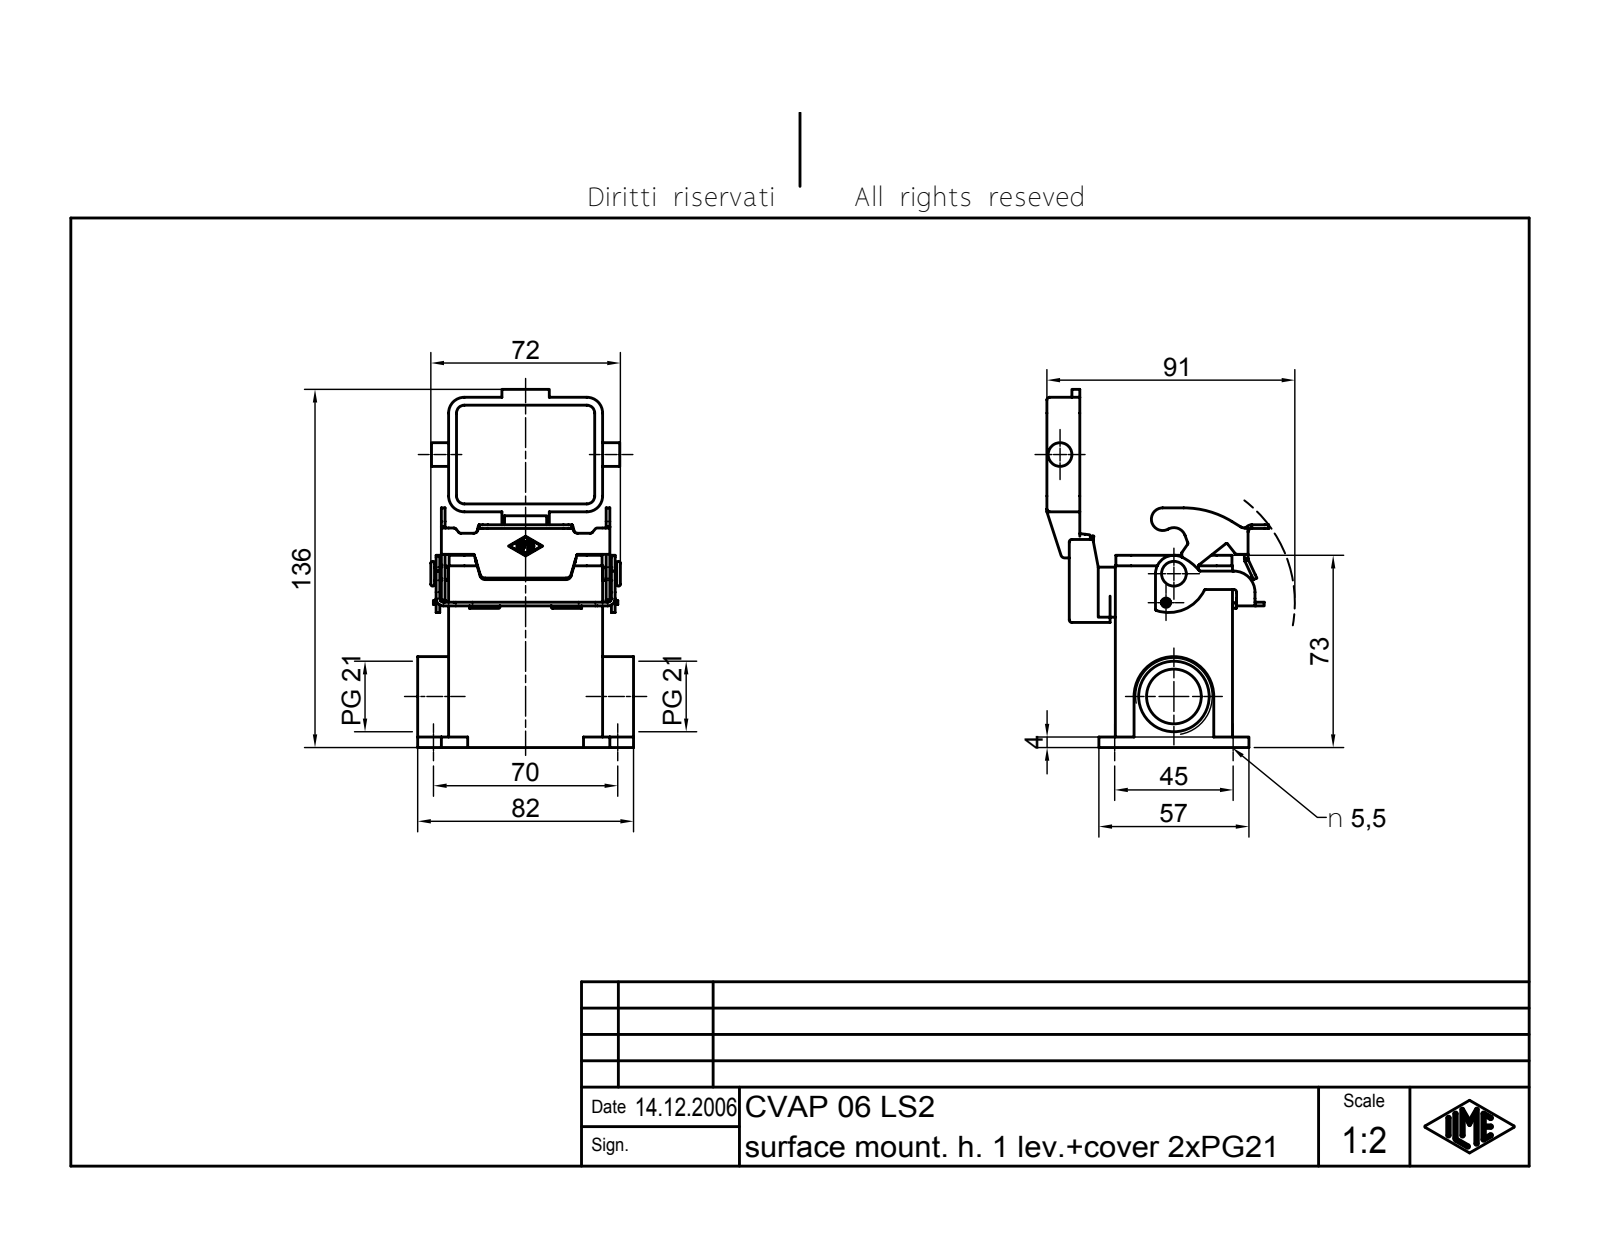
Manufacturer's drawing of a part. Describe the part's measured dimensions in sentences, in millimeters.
The part is named "CVAP 06 LS2". Its 3-D file was written by "Autodesk Inventor 7 (AUTOMOTIVE_DESIGN)". It is 4 solids with 572 faces: 222 planar, 185 cylindrical and 165 other. Overall it measures 136 by 84.23 by 82 millimeters. Its volume is 114 207 cubic millimeters and its surface area 62 745 square millimeters. Round holes: 4 of diameter 5.5, 1 of diameter 3.5, 1 of diameter 4, 1 of diameter 20.78, 1 of diameter 26.78. Round bosses or shafts: 2 of diameter 5, 1 of diameter 9, 1 of diameter 7, 1 of diameter 3.2, 1 of diameter 3. Partial cylindrical surfaces (rounded edges, fillets, slot ends): 27 of radius 1, 15 of radius 0.25, 10 of radius 0.5, 10 of radius 1.5, 8 of radius 6, 7 of radius 2, 6 of radius 1.4, 6 of radius 2.8. The main face-to-face distances are 4, 40.5, 44.5, 26, 30, 36.5, 70.5, 66.5, 10.75, 47.75. The hole center spacings are 45, 70, 83.22, 35.74.
